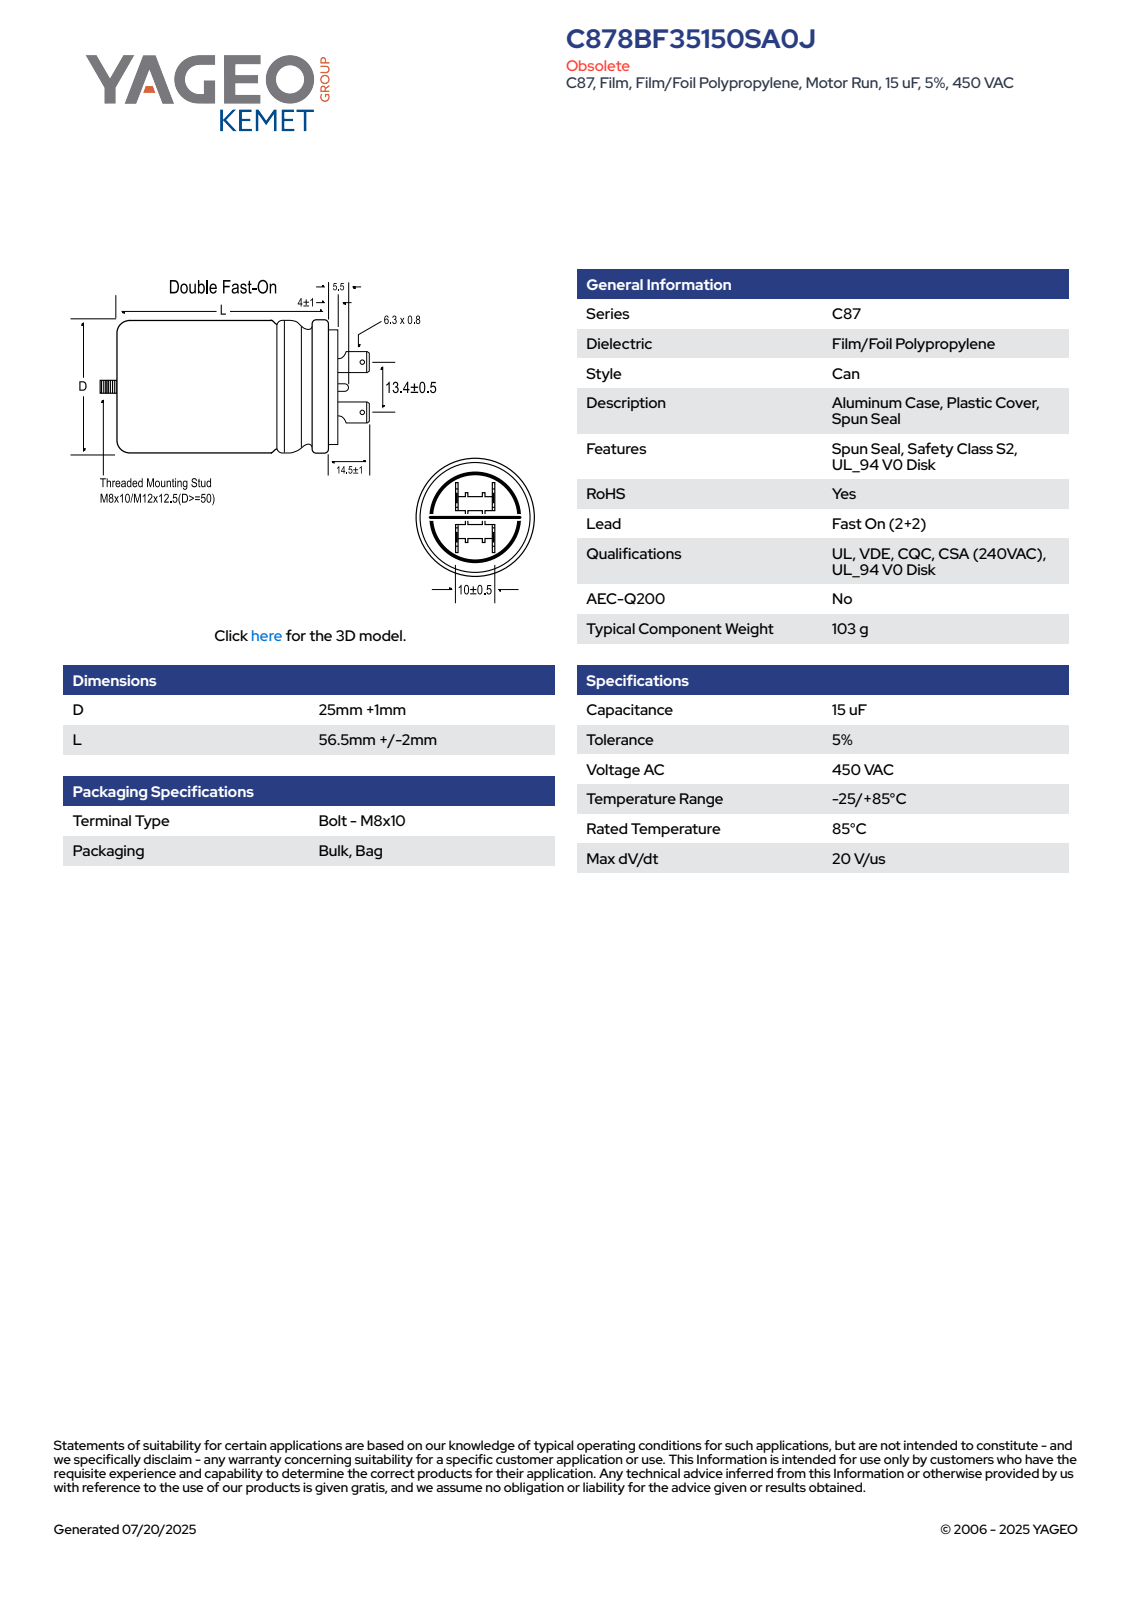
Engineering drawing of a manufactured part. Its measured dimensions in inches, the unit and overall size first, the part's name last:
Units: inches
Overall size (bounding box): 4.154 × 1.614 × 1.614
Round holes (diameter × count): ⌀0.047 ×2
Round bosses / shafts (diameter × count): ⌀1.614 ×1, ⌀1.378 ×1, ⌀0.315 ×1
Partial cylindrical surfaces — rounded edges, fillets, slot ends (radius × count): R0.01 ×9, R0.157 ×2, R0.807 ×1
Main face-to-face distances: 3.346, 2.919, 0.427, 0.031, 0.382, 0.413, 0.35, 3.15, 0.23, 0.197
Hole centre spacings: 0.547
Volume: 6.598 in³ · Surface area: 22.51 in²
Bodies: 1 solid, 156 faces (55 planar, 58 cylindrical, 43 other)
Part name (STEP PRODUCT): CFM_C87DF_40X78_D41L80
STEP written by: SolidWorks 2021 (AUTOMOTIVE_DESIGN)
